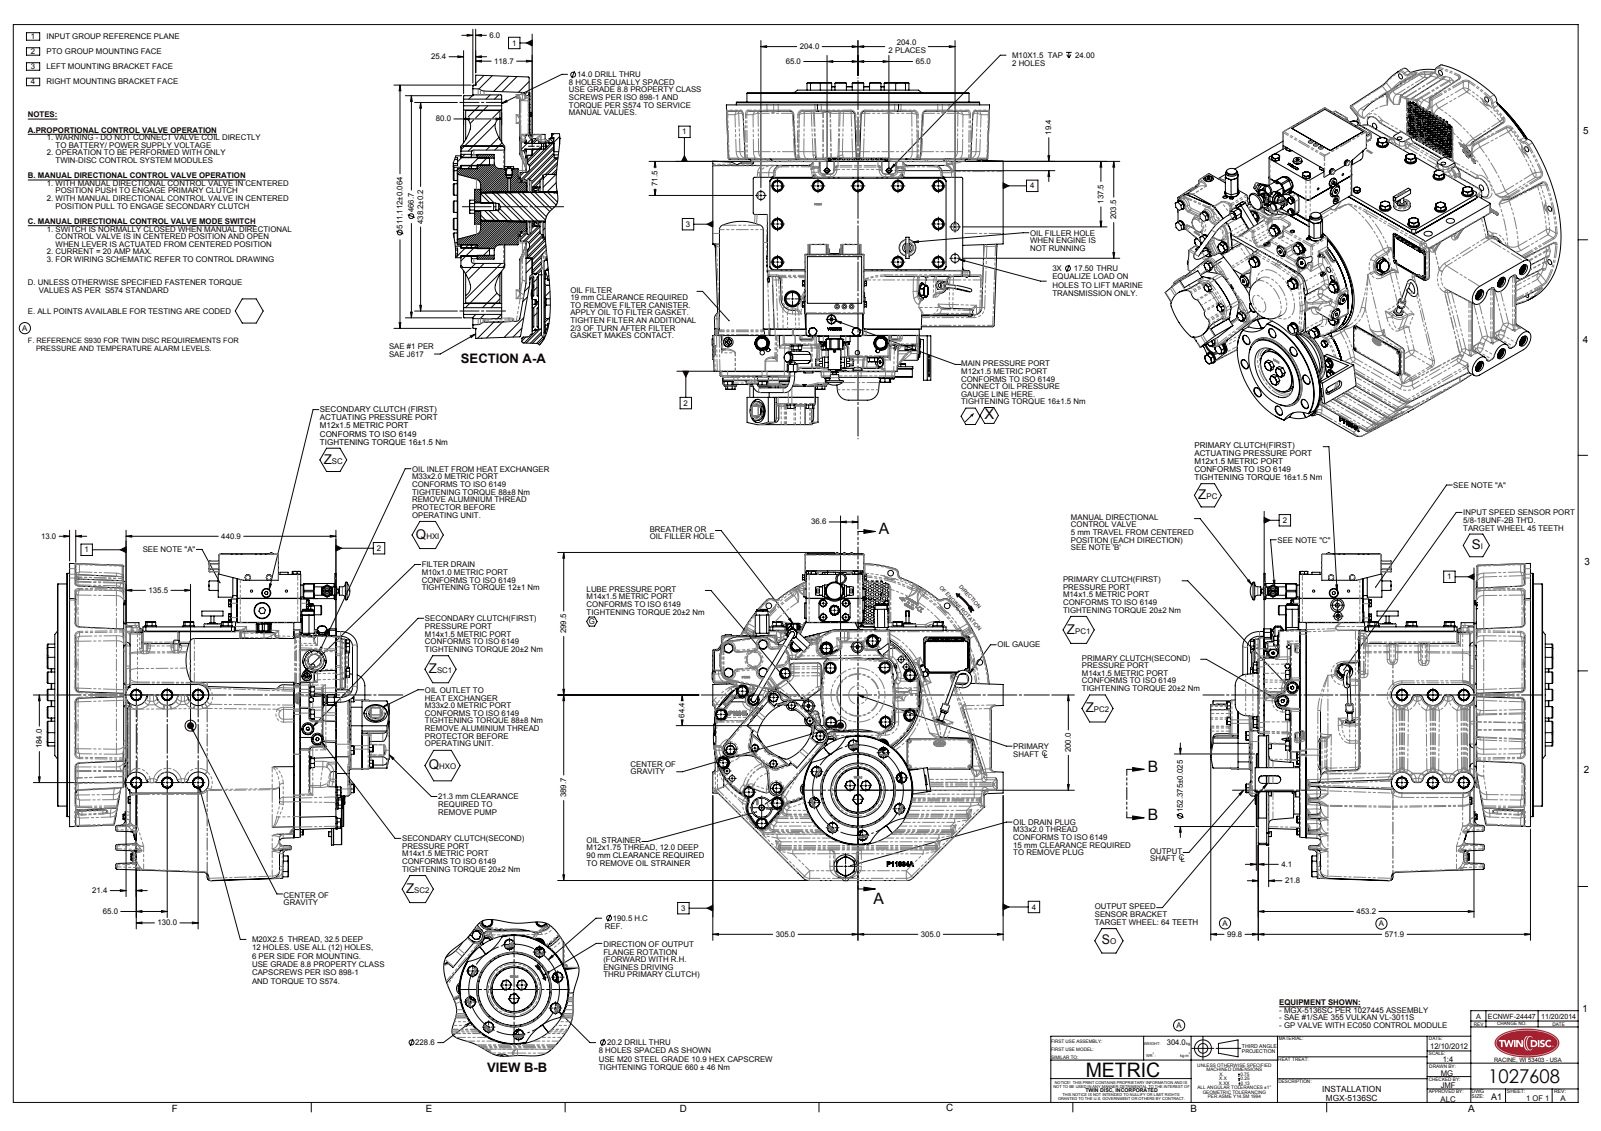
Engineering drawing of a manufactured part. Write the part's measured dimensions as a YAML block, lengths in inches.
part_name: "1027608"
step_written_by: "SolidWorks 2010 (AUTOMOTIVE_DESIGN)"
units: inches
bodies: {solids: 0, faces: 6492, planar: 2730, cylindrical: 1588, other: 2174}
overall_size: [28.296, 27.159, 24.113]
round_holes:
  - {diameter: 0.276, count: 81}
  - {diameter: 0.126, count: 22}
  - {diameter: 0.795, count: 14}
  - {diameter: 0.469, count: 12}
  - {diameter: 0.551, count: 8}
  - {diameter: 0.984, count: 8}
  - {diameter: 0.926, count: 5}
  - {diameter: 1.063, count: 5}
  - {diameter: 0.142, count: 4}
  - {diameter: 0.367, count: 4}
  - {diameter: 0.394, count: 4}
  - {diameter: 0.512, count: 4}
round_bosses_or_shafts:
  - {diameter: 0.945, count: 44}
  - {diameter: 0.748, count: 8}
  - {diameter: 0.472, count: 7}
  - {diameter: 0.394, count: 6}
  - {diameter: 0.1, count: 5}
  - {diameter: 0.781, count: 4}
  - {diameter: 0.75, count: 3}
  - {diameter: 0.512, count: 3}
partial_cylinders:
  - {radius: 0.118, count: 140}
  - {radius: 0.315, count: 79}
  - {radius: 0.256, count: 58}
  - {radius: 0.098, count: 50}
  - {radius: 0.197, count: 44}
  - {radius: 0.63, count: 26}
  - {radius: 0.12, count: 24}
  - {radius: 0.079, count: 20}
face_to_face_distances: [0.015, 0.515, 0.531, 2.968, 2.953, 3.483, 17.867, 14.914, 14.899, 14.383]
hole_center_spacings: [0.681, 0.339, 0.343, 1.02, 1.362, 3.75, 7.048, 3.75]
